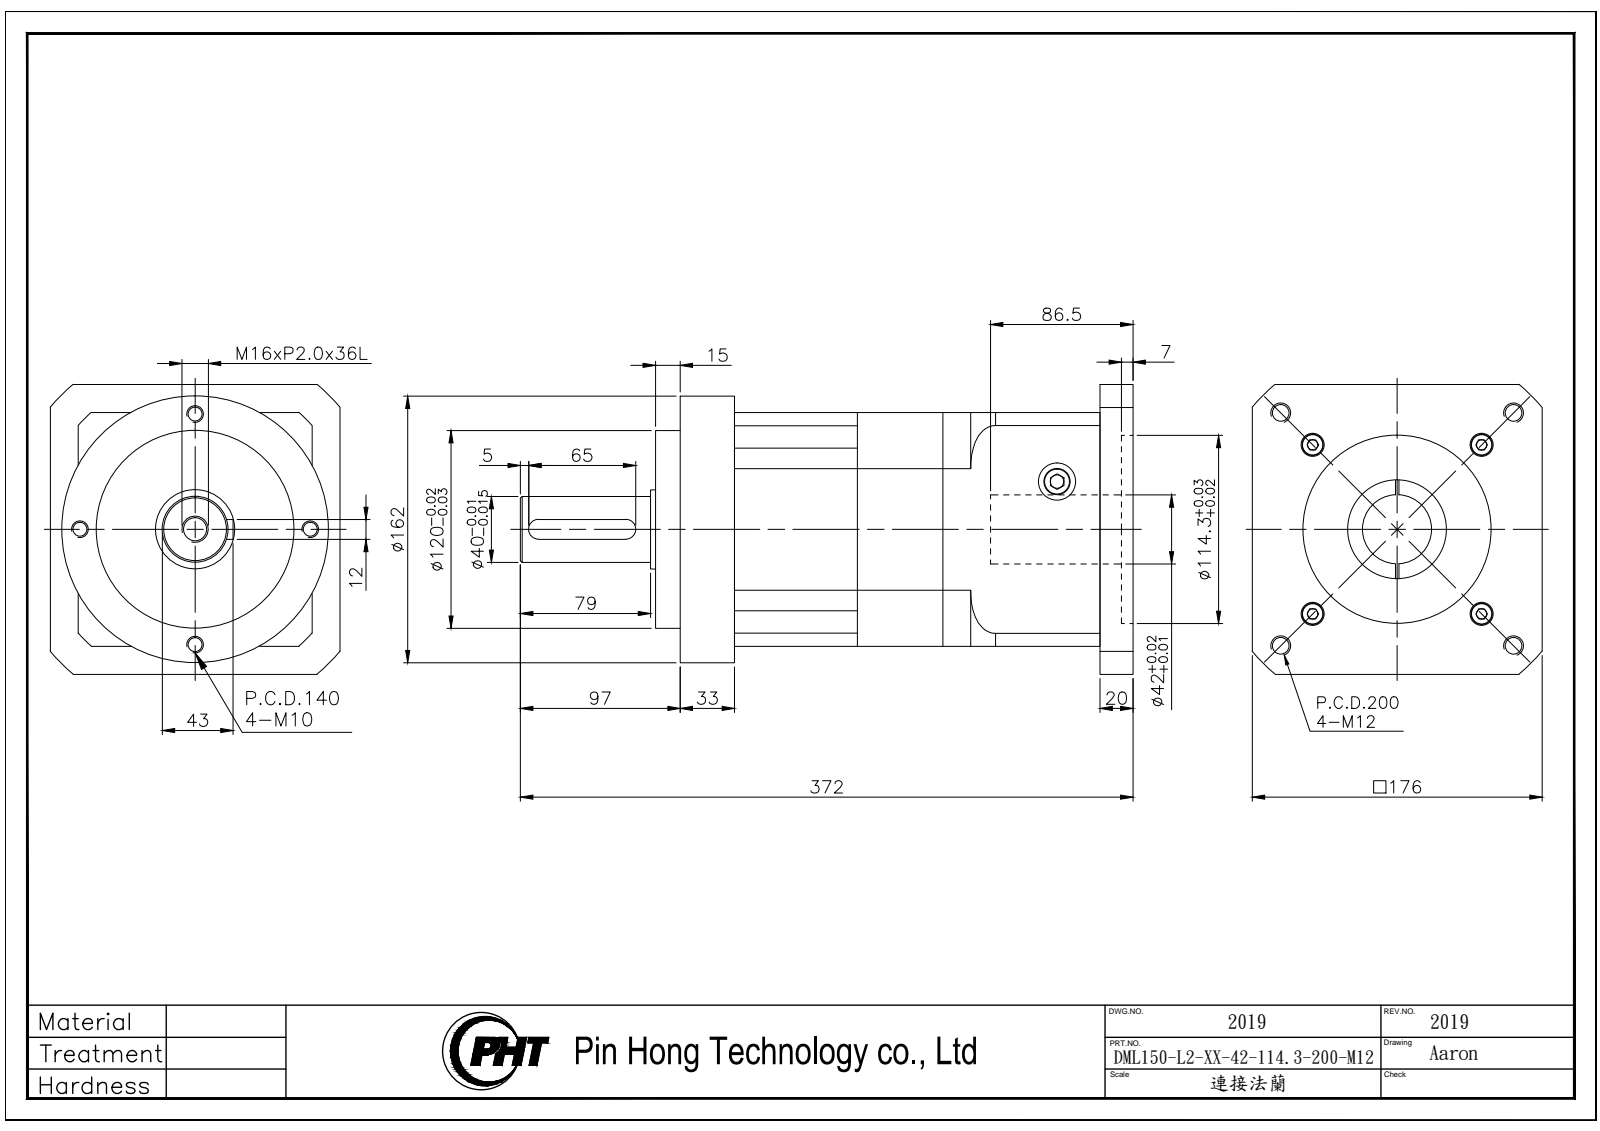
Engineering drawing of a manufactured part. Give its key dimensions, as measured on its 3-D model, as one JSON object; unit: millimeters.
{"part_name": "DML150-L2-XX-42-114.3-200-M12_2019", "step_written_by": "SolidWorks 2016 (AUTOMOTIVE_DESIGN)", "units": "millimeters", "bodies": {"solids": 4, "faces": 384, "planar": 177, "cylindrical": 159, "other": 48}, "overall_size": [372, 176, 176], "volume_mm3": 5218000, "surface_area_mm2": 445112, "round_holes": [[14, 13], [9, 12], [6.8, 4], [8.5, 4], [10.2, 4], [22.5, 2], [42, 1], [60, 1], [92, 1], [110, 1], [114.3, 1]], "round_bosses_or_shafts": [[13, 12], [162, 1], [120, 1], [74, 1], [48, 1], [40, 1]], "partial_cylinders_radius": [[10, 4], [6, 2], [80, 1], [95, 1], [115, 1]], "face_to_face_distances": [142, 74.7, 51.8, 126.5, 115.5, 167.3, 242, 20, 17, 159], "hole_center_spacings": [71, 18.79, 36.4, 36.51, 54.58, 70.51, 70.71, 87.37]}
